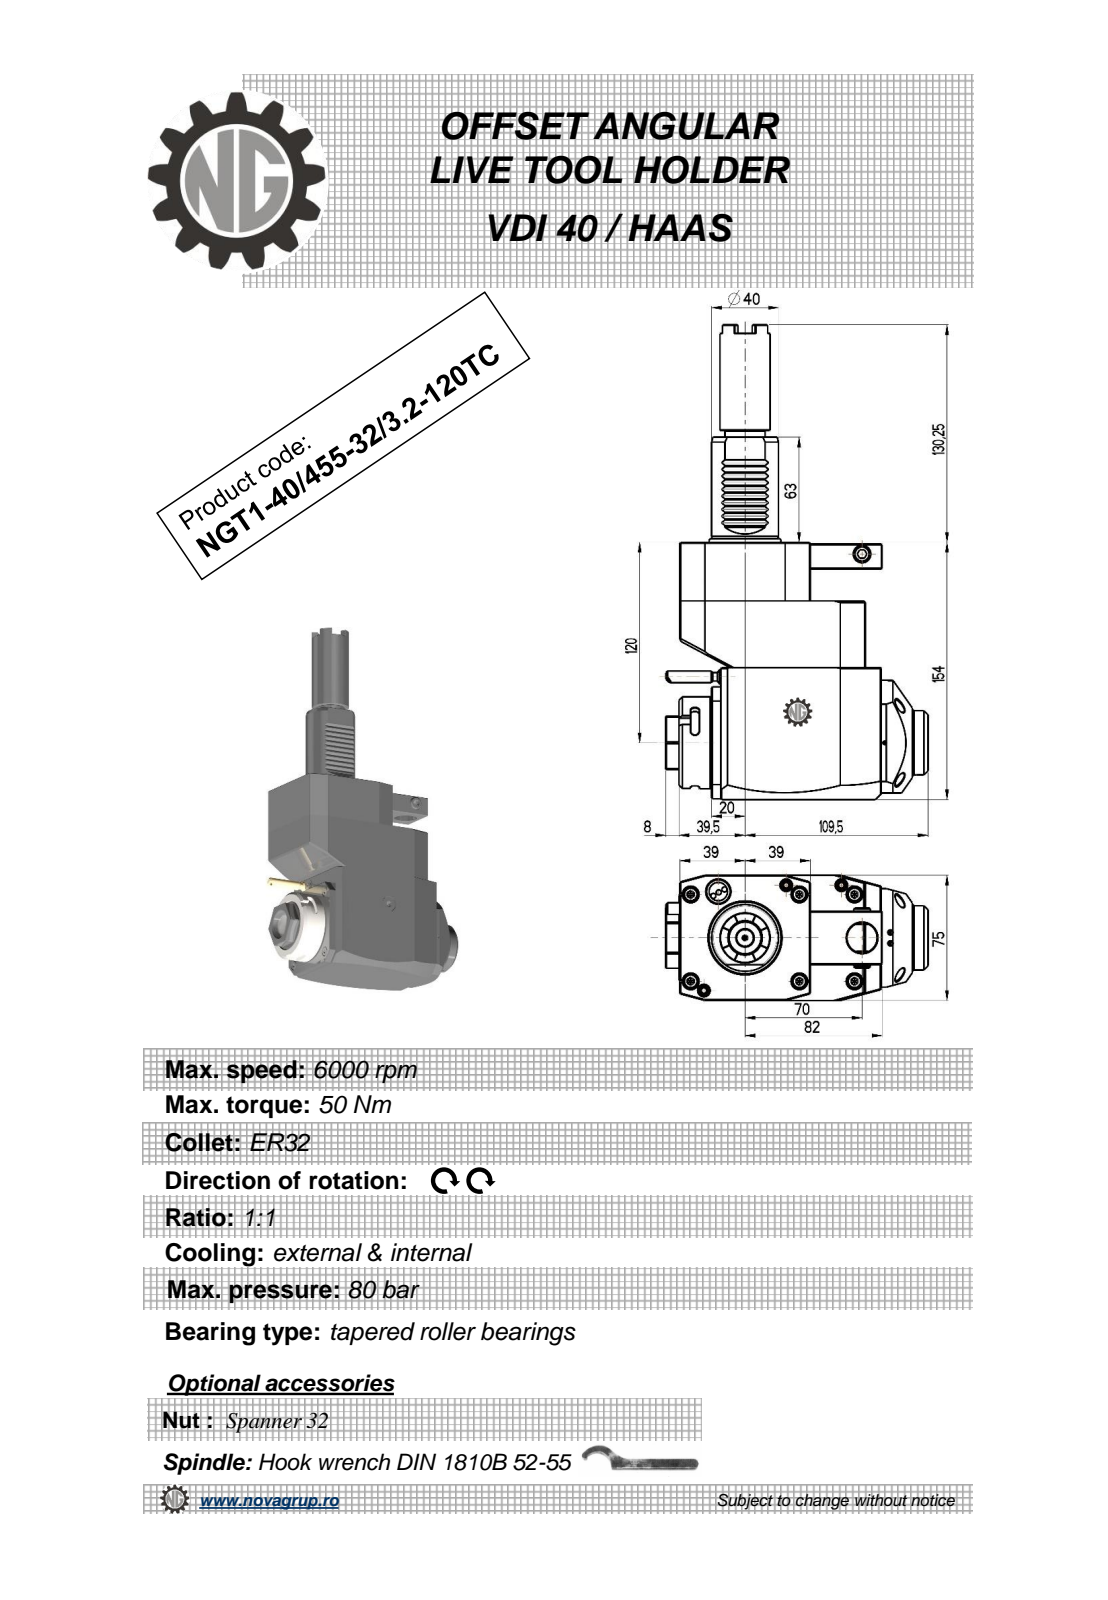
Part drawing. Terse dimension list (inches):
name: NGT1_40_455_32_3_2_120TC
written by: PRO/ENGINEER BY PARAMETRIC TECHNOLOGY CORPORATION, 2010280 (CONFIG_CONTROL_DESIGN)
unit: in
bodies: 1 solid, 374 faces (222 planar, 66 cylindrical, 86 other)
size: 11.191 × 6.181 × 2.953
volume: 81.22 in³; area: 153.5 in²
holes: 1× ⌀0.098, 1× ⌀0.118, 1× ⌀0.374, 1× ⌀0.709, 1× ⌀0.787, 1× ⌀0.906
bosses: 2× ⌀0.353, 1× ⌀2.165, 1× ⌀1.89, 1× ⌀1.575, 1× ⌀1.516, 1× ⌀1.181, 1× ⌀0.945, 1× ⌀0.394
rounds: 10× R0.012, 6× R0.098, 2× R7.087, 1× R0.02, 1× R0.167, 1× R0.965, 1× R1.476
face distances: 2.953, 6.063, 0.748, 2.323, 0.02, 4.37, 3.622, 1.378, 4.685, 2.106
hole spacings: 1.701, 2.756, 2.956, 4.429
